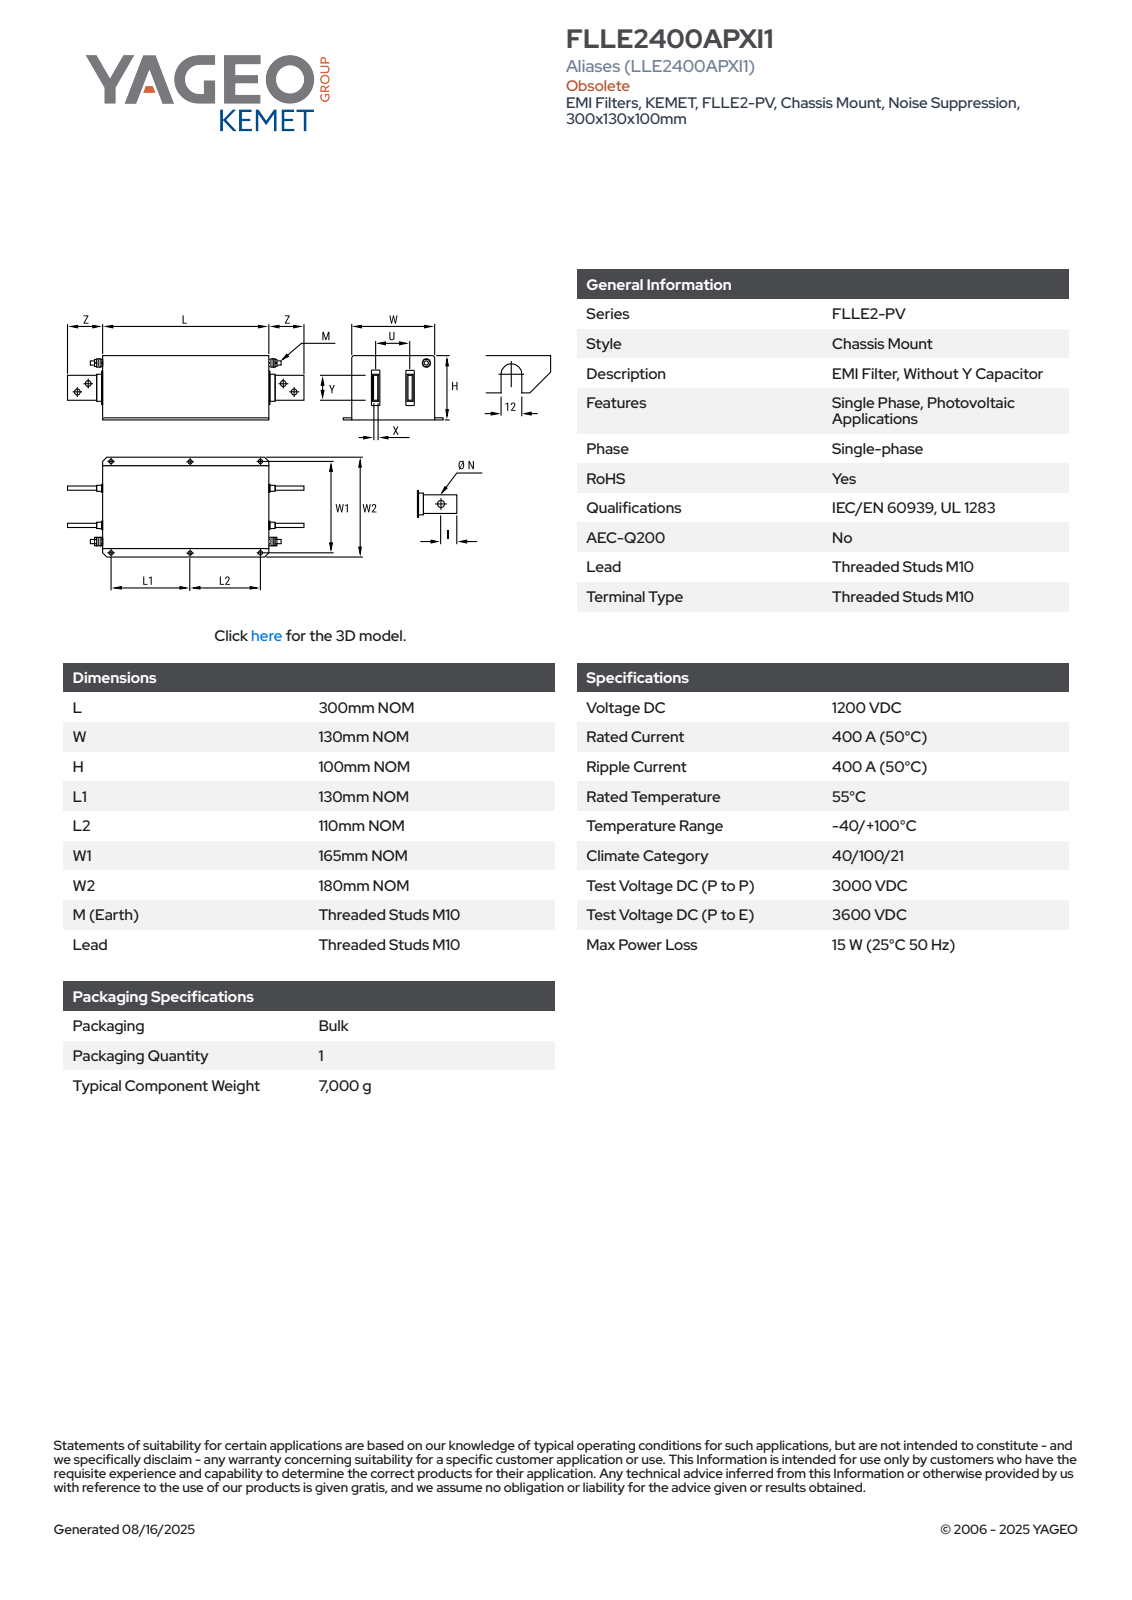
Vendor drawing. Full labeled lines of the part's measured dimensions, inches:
Part name (STEP PRODUCT): 094-00280 Case 600A DC RevC; HEX BOLT M10x35_91280A636; FLLE2400APVI1_EXT; WASHER M10 Ø20_93475A280 (+8 more)
STEP written by: SolidWorks 2021 (AUTOMOTIVE_DESIGN)
Units: inches
Bodies: 56 solids, 1962 faces (500 planar, 588 cylindrical, 874 other)
Overall size (bounding box): 16.378 × 7.087 × 3.937
Volume: 25.44 in³ · Surface area: 709.8 in²
Round holes (diameter × count): ⌀0.071 ×12, ⌀0.134 ×8, ⌀0.126 ×4, ⌀0.413 ×3, ⌀0.472 ×1
Round bosses / shafts (diameter × count): ⌀0.126 ×8, ⌀0.787 ×1, ⌀0.394 ×1
Partial cylindrical surfaces — rounded edges, fillets, slot ends (radius × count): R0.079 ×56, R0.02 ×46, R0.01 ×22, R0.039 ×22, R0.098 ×10, R0.236 ×6, R0.059 ×4, R0.118 ×2
Main face-to-face distances: 0.079, 0.039, 5.039, 3.858, 3.937, 3.819, 3.898, 11.732, 4.961, 5.118
Hole centre spacings: 1.039, 1.057, 1.398, 1.463, 2.165, 2.313, 2.323, 2.756
